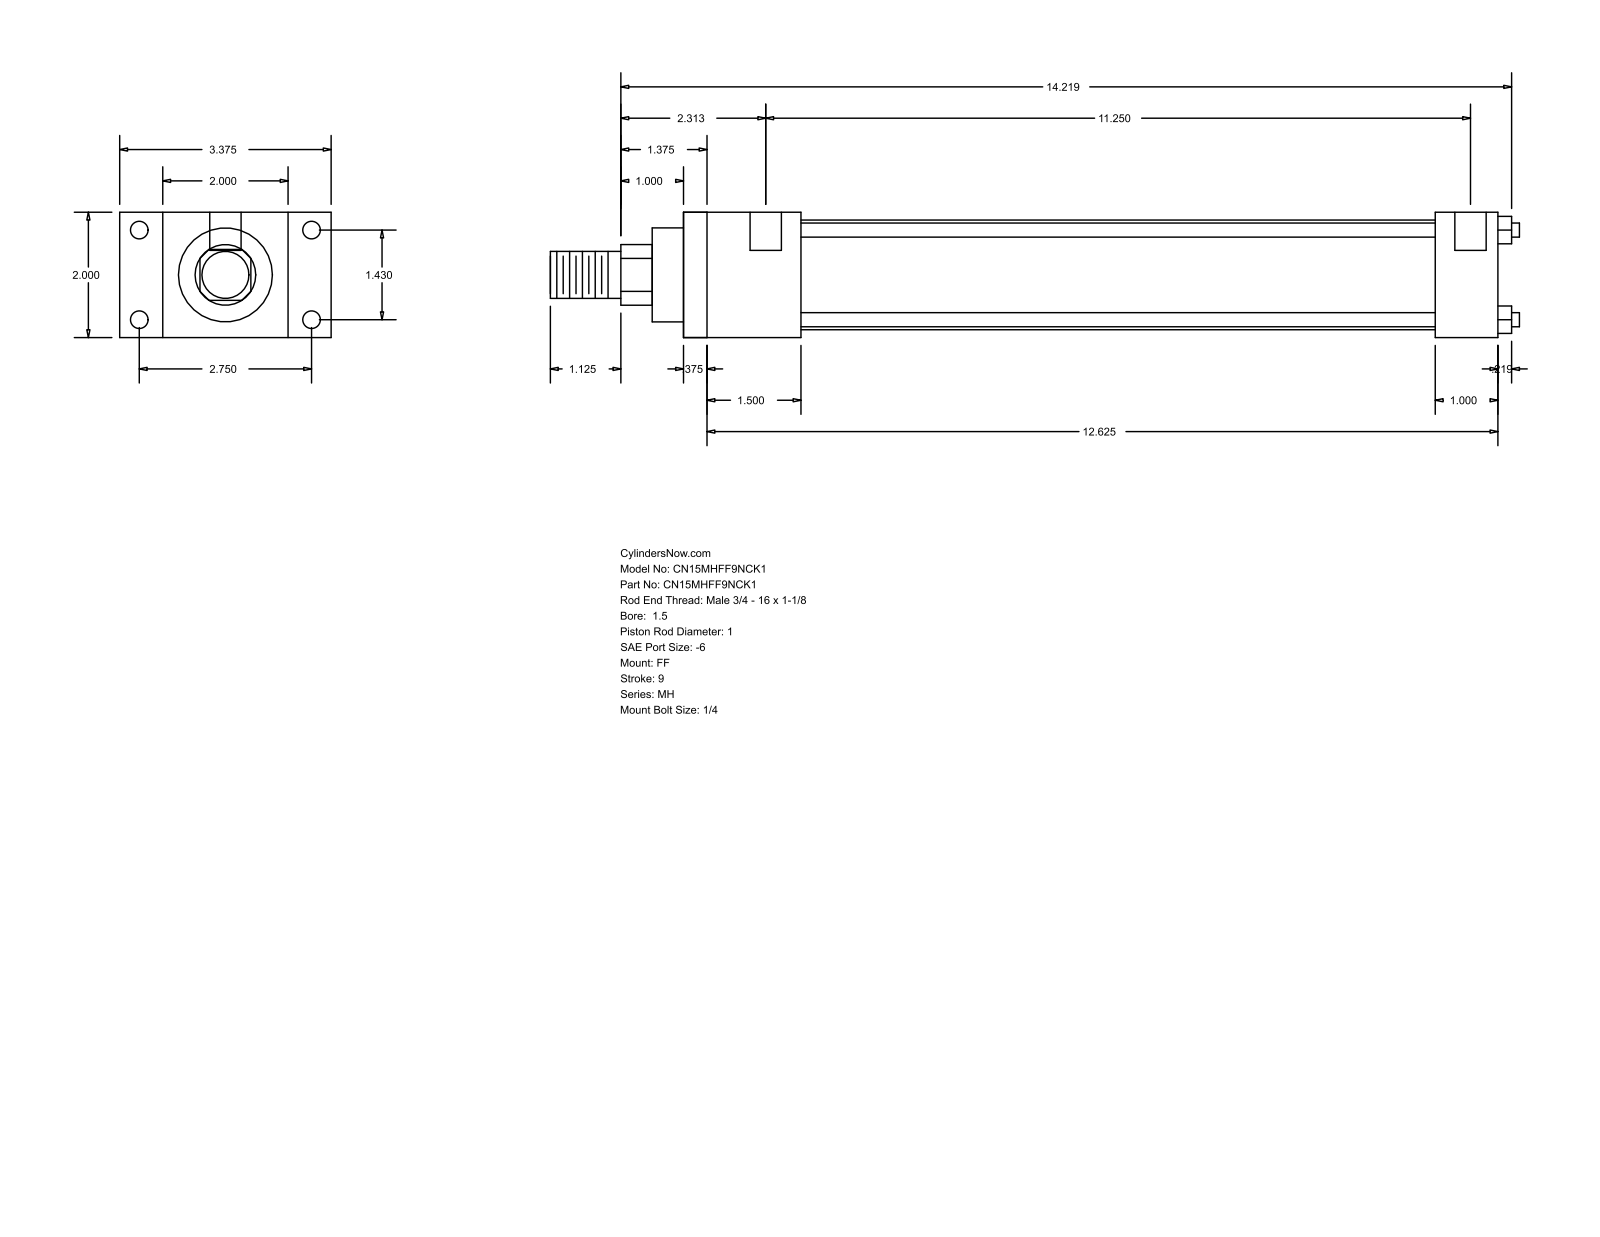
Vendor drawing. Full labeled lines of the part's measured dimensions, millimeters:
Part name (STEP PRODUCT): MH_FF__0150_1
STEP written by: GSSL Pune (CONFIG_CONTROL_DESIGN)
Units: millimetres
Bodies: 0 solids, 92 faces (64 planar, 28 cylindrical, 0 other)
Overall size (bounding box): 392.91 × 85.72 × 50.8
Round holes (diameter × count): ⌀5.56 ×4, ⌀7.14 ×4, ⌀12.7 ×2
Round bosses / shafts (diameter × count): ⌀5.71 ×4, ⌀44.45 ×1, ⌀38.1 ×1, ⌀25.4 ×1, ⌀19.05 ×1
Partial cylindrical surfaces — rounded edges, fillets, slot ends (radius × count): R12.29 ×1
Main face-to-face distances: 50.8, 330.2, 9.52, 320.68, 25.4, 17.46, 68.26, 47.63, 38.11, 282.57
Hole centre spacings: 36.32, 69.84, 78.72, 288.93, 3.18, 285.75
